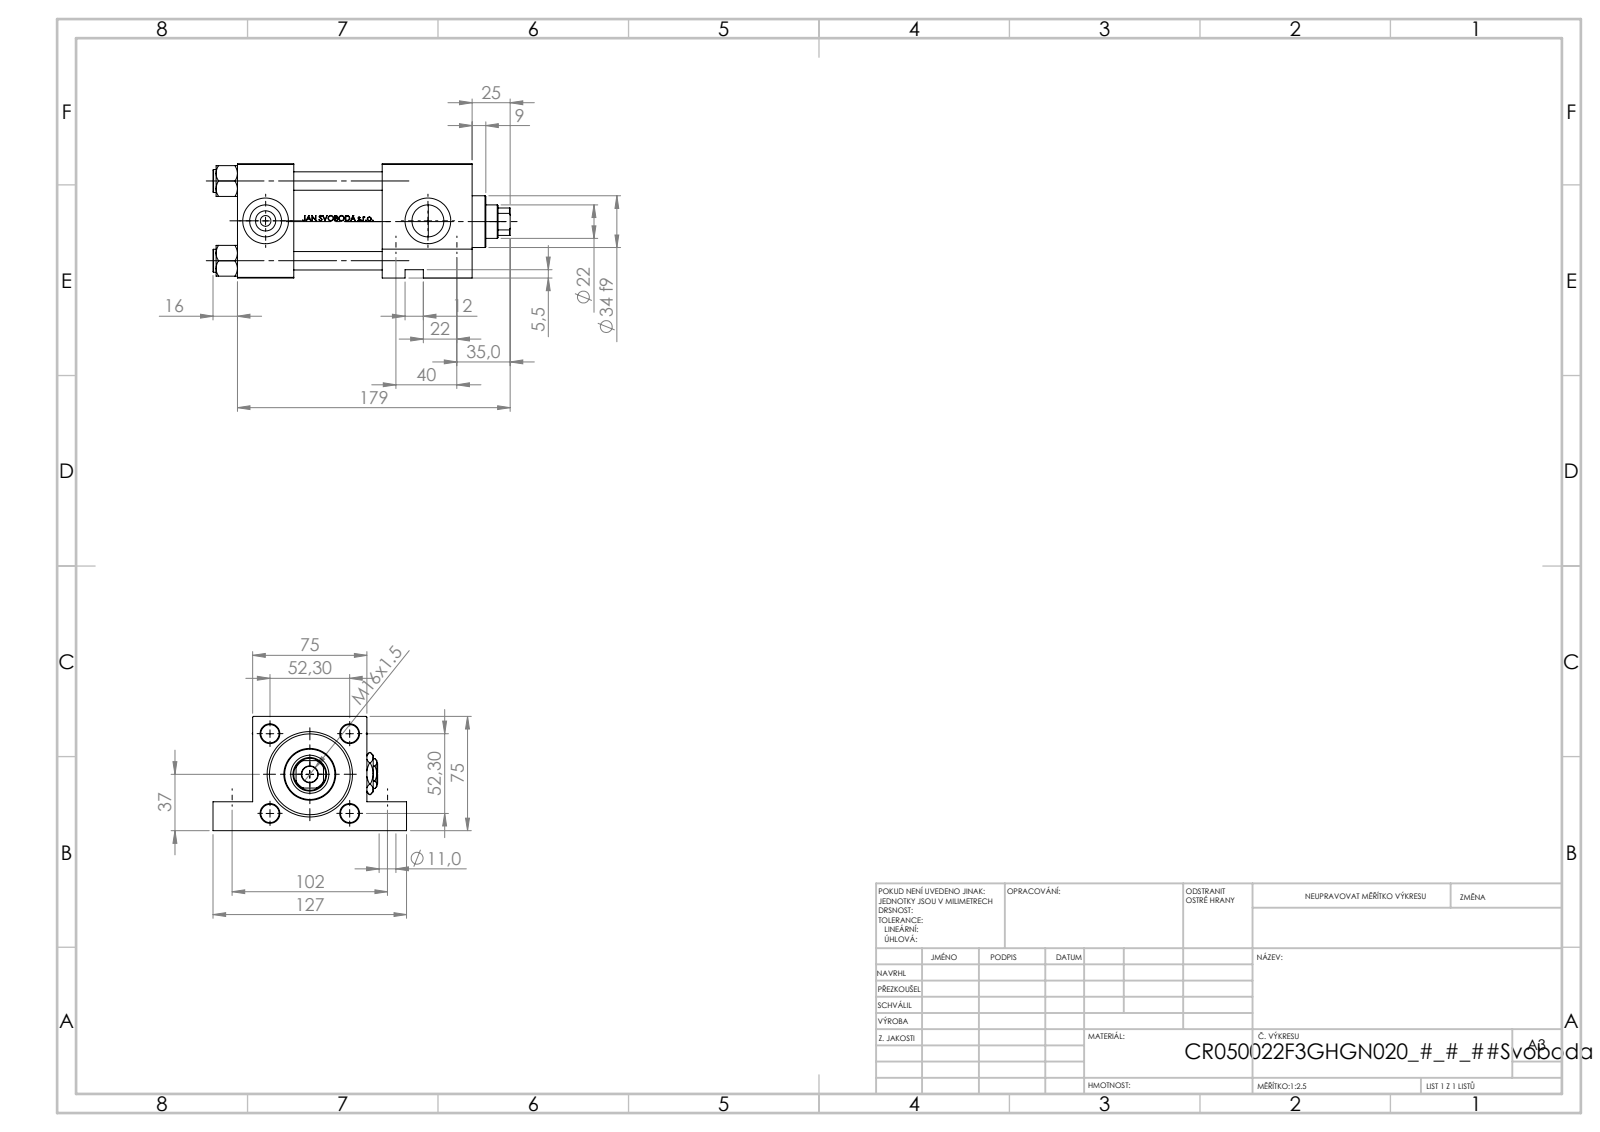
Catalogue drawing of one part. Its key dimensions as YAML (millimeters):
part_name: "V215CR_VCP_F; V215CR_F_TYCINKA; V215_VC_A; NUT_M5_F (+2 more)"
step_written_by: "SolidWorks 2019 (CONFIG_CONTROL_DESIGN)"
units: millimeters
bodies: {solids: 13, faces: 1199, planar: 483, cylindrical: 134, other: 582}
overall_size: [195, 127, 75]
volume: 702130
surface_area: 160606
round_holes:
  - {diameter: 12, count: 4}
  - {diameter: 20.96, count: 3}
  - {diameter: 30, count: 3}
  - {diameter: 7, count: 2}
  - {diameter: 11, count: 2}
  - {diameter: 11, count: 2}
  - {diameter: 10.5, count: 1}
  - {diameter: 17, count: 1}
  - {diameter: 22, count: 1}
  - {diameter: 25, count: 1}
  - {diameter: 41, count: 1}
  - {diameter: 50, count: 1}
round_bosses_or_shafts:
  - {diameter: 15, count: 4}
  - {diameter: 56, count: 1}
  - {diameter: 34, count: 1}
partial_cylinders:
  - {radius: 10.5, count: 1}
face_to_face_distances: [75, 37, 154, 117, 95, 58, 59, 19, 56, 125.3]
hole_center_spacings: [52.3, 36.63, 37.34, 40, 73.96, 102, 109.56, 13]
